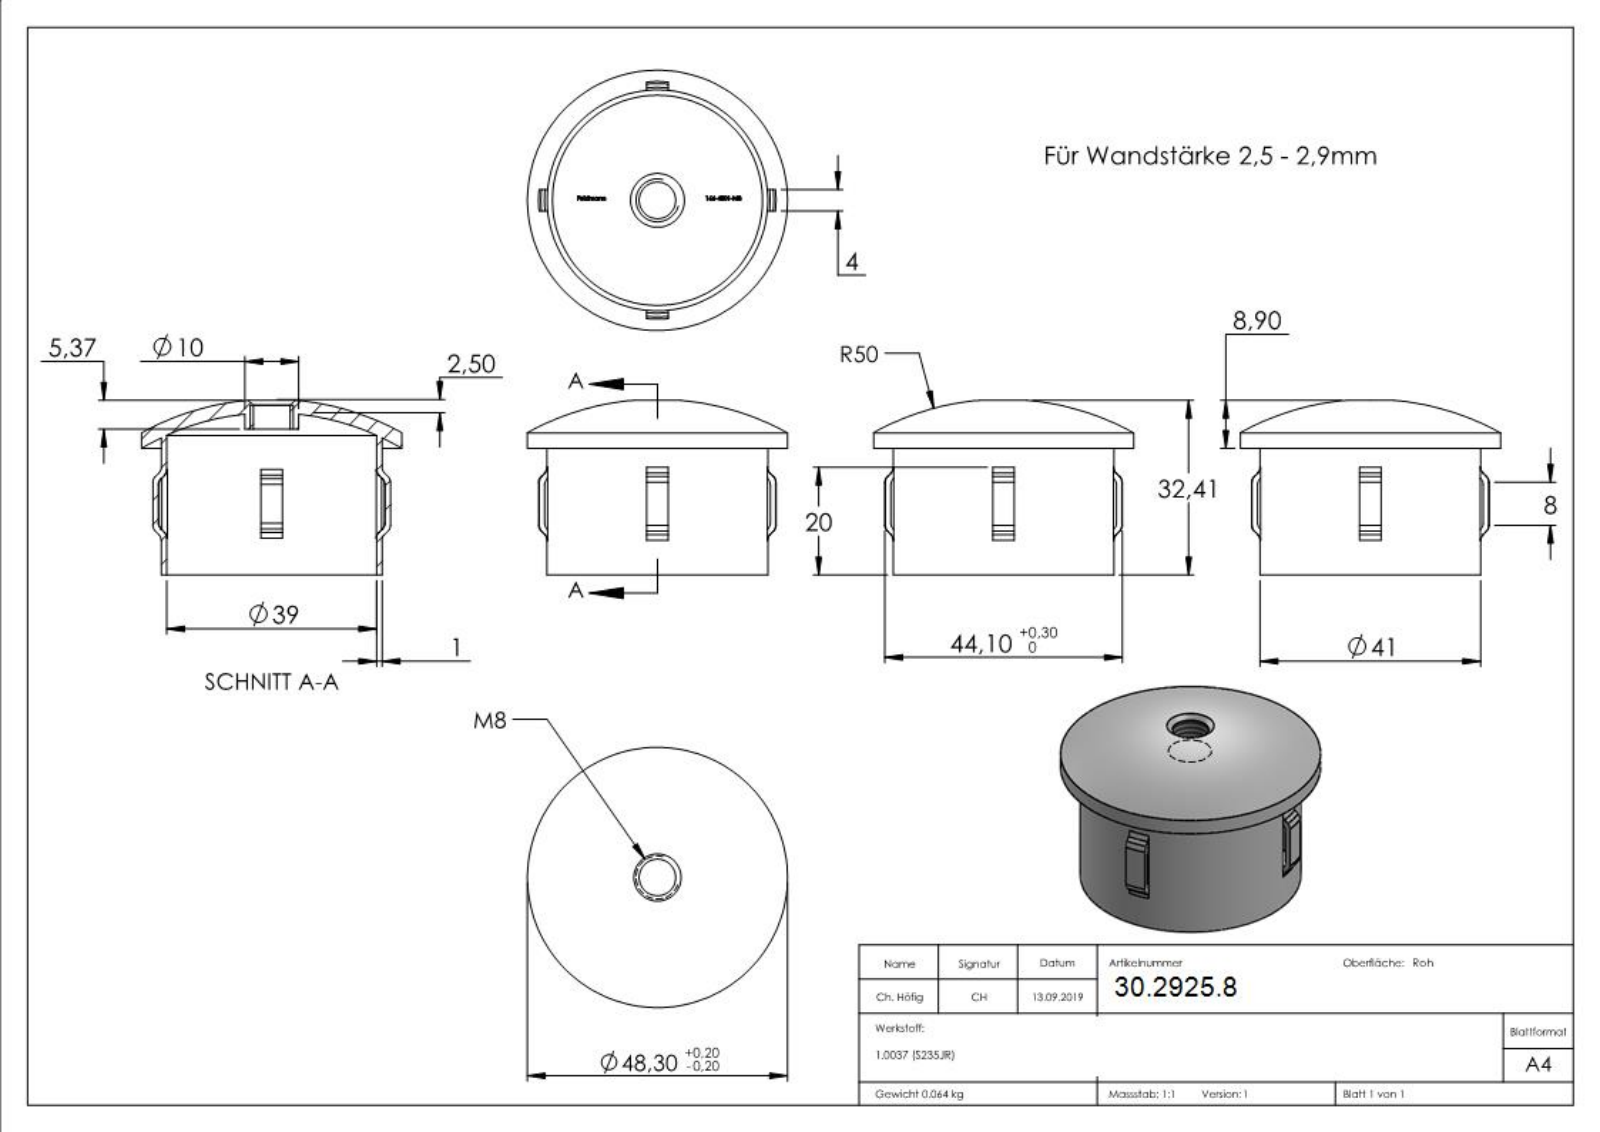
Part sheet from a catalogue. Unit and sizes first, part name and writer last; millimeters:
Units: millimetres
Overall size (bounding box): 48.3 × 48.3 × 32.41
Round holes (diameter × count): ⌀6.8 ×1, ⌀39 ×1
Round bosses / shafts (diameter × count): ⌀48.3 ×1, ⌀41 ×1, ⌀10 ×1
Partial cylindrical surfaces — rounded edges, fillets, slot ends (radius × count): R21.05 ×1, R22.05 ×1
Main face-to-face distances: 4, 27.03, 2, 1.21, 0.83, 0.44, 26.85, 22.82, 4.03, 1.78
Volume: 8 170 mm³ · Surface area: 11 139 mm²
Bodies: 1 solid, 367 faces (124 planar, 20 cylindrical, 223 other)
Part name (STEP PRODUCT): 166-4801-M8
STEP written by: SolidWorks 2015 (CONFIG_CONTROL_DESIGN)
